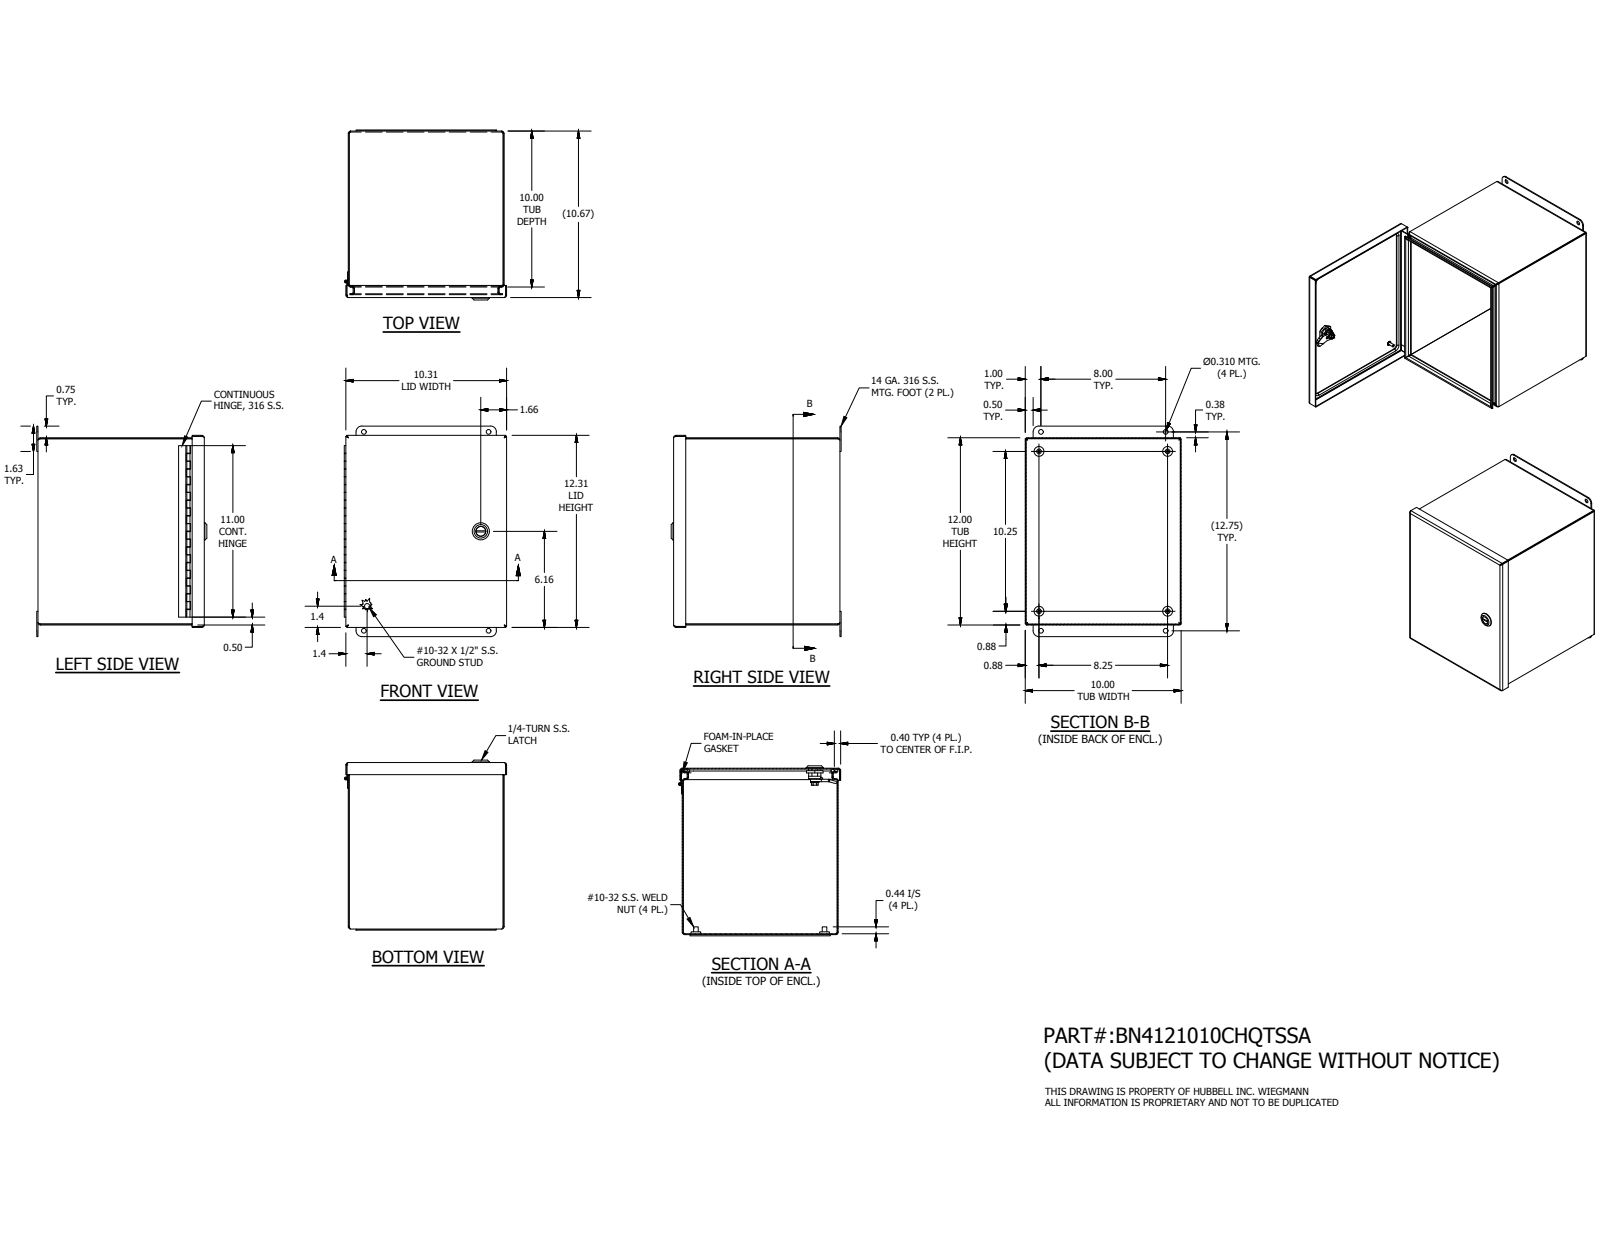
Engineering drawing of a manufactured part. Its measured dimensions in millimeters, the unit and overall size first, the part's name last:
Units: millimetres
Overall size (bounding box): 342.9 × 276.99 × 264.46
Round holes (diameter × count): ⌀3.96 ×4, ⌀7.87 ×4, ⌀2.96 ×1, ⌀5 ×1, ⌀8 ×1, ⌀10 ×1, ⌀10.2 ×1, ⌀16.1 ×1, ⌀20.38 ×1
Round bosses / shafts (diameter × count): ⌀15.88 ×4, ⌀7.62 ×4, ⌀28 ×1, ⌀19.8 ×1, ⌀16 ×1, ⌀15.2 ×1, ⌀13.5 ×1, ⌀12.8 ×1
Partial cylindrical surfaces — rounded edges, fillets, slot ends (radius × count): R2.38 ×20, R3.88 ×20, R3.17 ×16, R0.5 ×8, R4 ×4, R9.53 ×4, R2.31 ×2, R6.45 ×1
Main face-to-face distances: 1.5, 1.49, 303.3, 269.59, 252.5, 271.08, 254, 252.51, 251.01, 268.09
Hole centre spacings: 31.91, 292.12, 357.65, 131.14, 203.2, 208.8, 208.81, 209.55
Volume: 846 903 mm³ · Surface area: 1 077 000 mm²
Bodies: 21 solids, 671 faces (366 planar, 208 cylindrical, 97 other)
Part name (STEP PRODUCT): BN41210CHQTSSALID; 12x10; 348130; 32884LH (+8 more)
STEP written by: Autodesk Inventor 2016 (AUTOMOTIVE_DESIGN)
